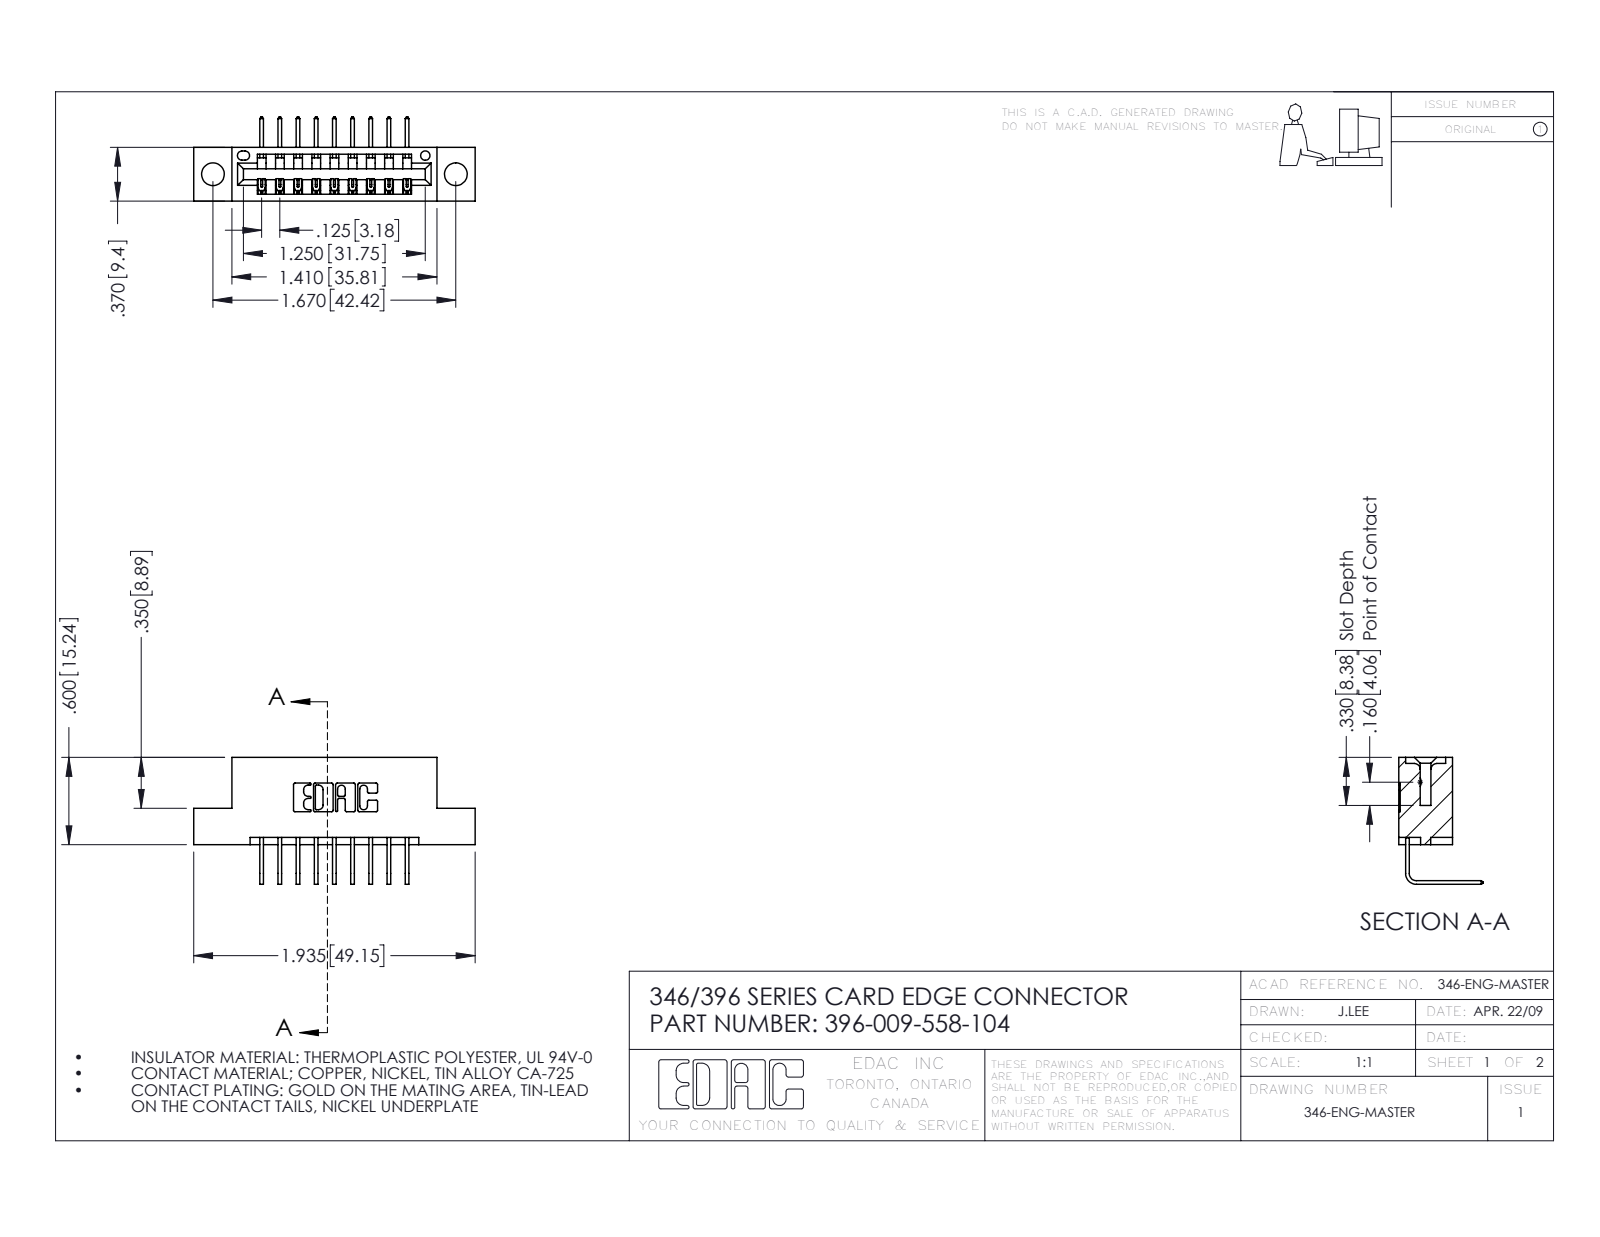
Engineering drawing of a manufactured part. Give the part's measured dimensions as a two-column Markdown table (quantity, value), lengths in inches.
| quantity | value |
| --- | --- |
| part name | 346 Part_Flush Mounting Lugs - 0.156 Dia-TH; 396-009-558-104; 345-292-001_558 Tail - 2 |
| STEP written by | SolidWorks 2016 (CONFIG_CONTROL_DESIGN) |
| units | inches |
| bodies | 10 solids, 662 faces (454 planar, 208 cylindrical, 0 other) |
| overall size | 1.935 × 0.873 × 0.58 |
| volume | 0.27 in³ |
| surface area | 7.985 in² |
| round holes (diameter × count) | 0.156 × 2, 0.064 × 1 |
| partial cylindrical surfaces (radius × count) | 0.01 × 22, 0.006 × 18, 0.007 × 6, 0.031 × 6, 0.026 × 3, 0.031 × 2, 0.04 × 2, 0.014 × 1 |
| main face-to-face distances | 0.25, 0.322, 0.37, 0.048, 0.298, 0.025, 0.148, 0.222, 0.1, 0.174 |
| hole center spacings | 0.246, 1.465, 1.67 |
